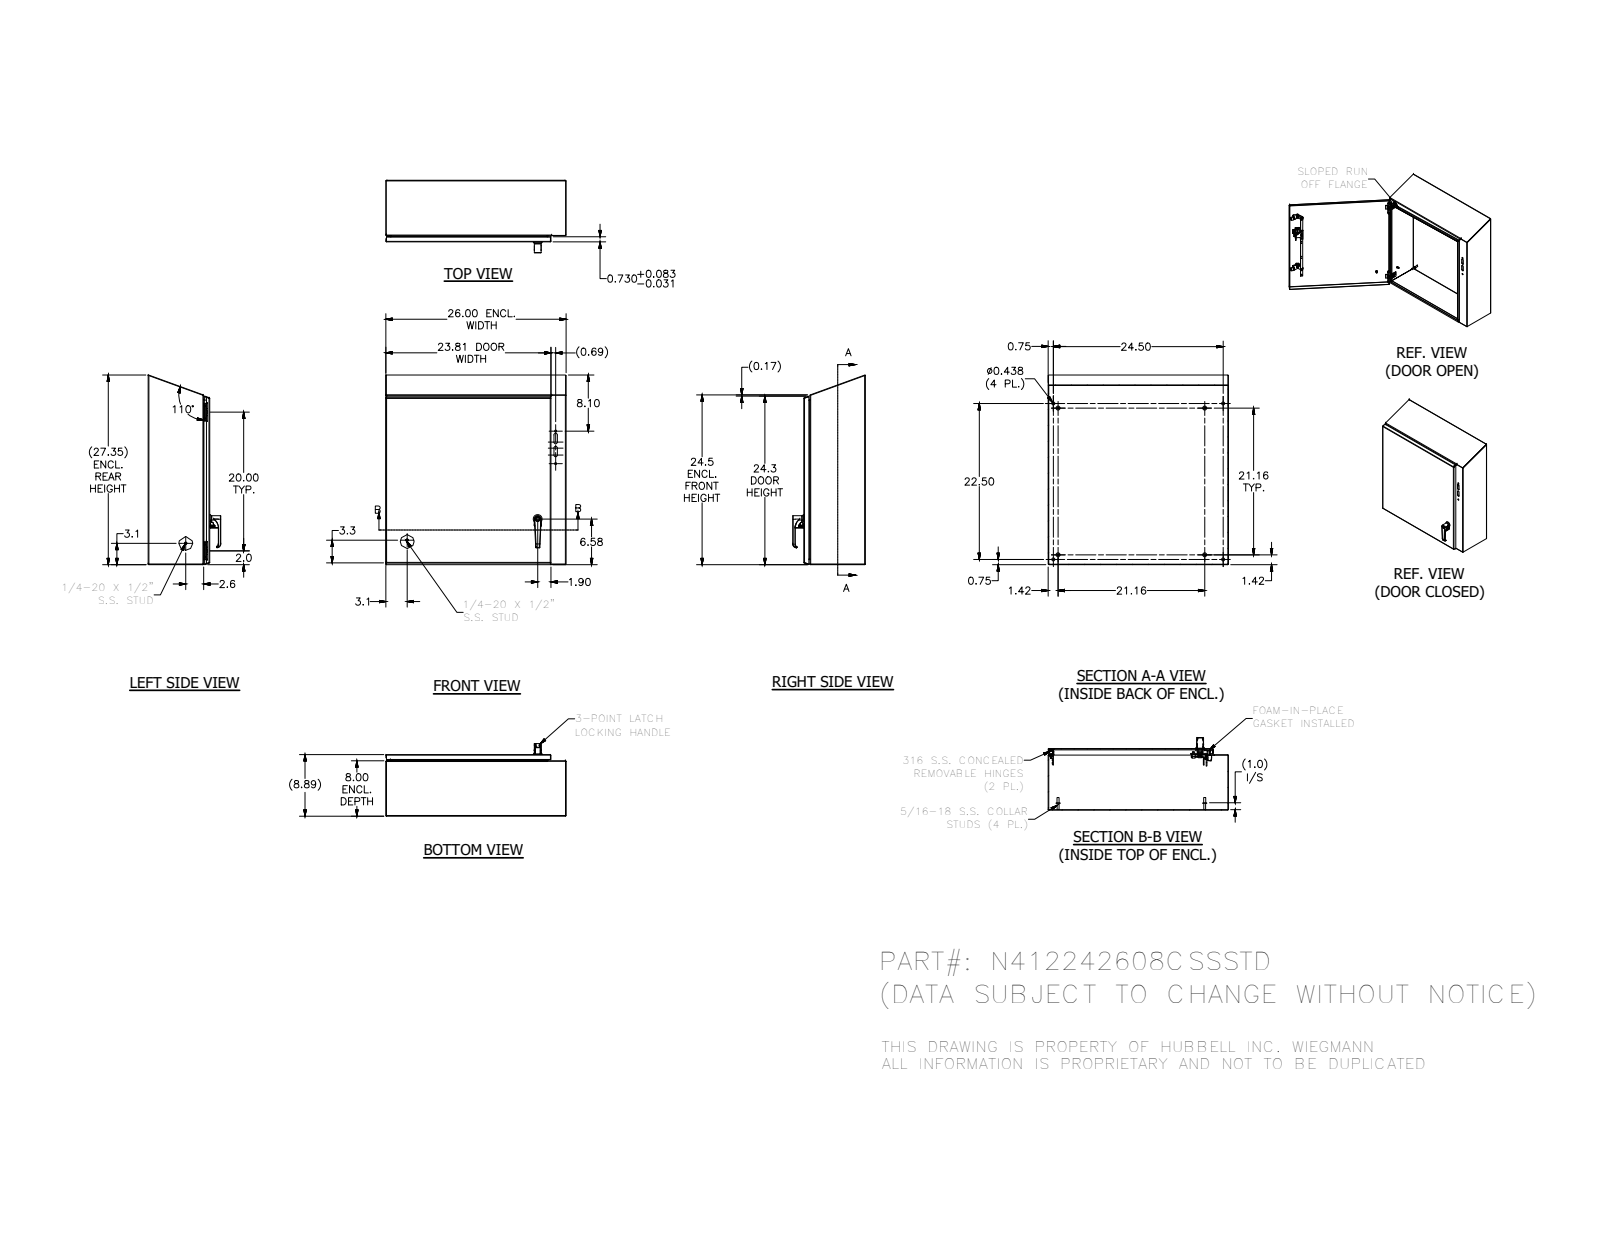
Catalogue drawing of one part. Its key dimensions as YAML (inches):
part_name: "N412242608CSSSTDB3S; 388151; N4122608CSSSTDTOP; 38846 (+8 more)"
step_written_by: "Autodesk Inventor 2016 (AUTOMOTIVE_DESIGN)"
units: inches
bodies: {solids: 62, faces: 2130, planar: 858, cylindrical: 747, other: 525}
overall_size: [27.348, 26, 10.481]
volume: 178.2
surface_area: 4883
round_holes:
  - {diameter: 0.145, count: 6}
  - {diameter: 0.156, count: 5}
  - {diameter: 0.093, count: 4}
  - {diameter: 0.152, count: 4}
  - {diameter: 0.167, count: 4}
  - {diameter: 0.172, count: 4}
  - {diameter: 0.187, count: 4}
  - {diameter: 0.437, count: 4}
  - {diameter: 0.32, count: 3}
  - {diameter: 0.196, count: 2}
  - {diameter: 0.211, count: 2}
  - {diameter: 0.22, count: 2}
round_bosses_or_shafts:
  - {diameter: 0.25, count: 12}
  - {diameter: 0.3, count: 8}
  - {diameter: 0.563, count: 4}
  - {diameter: 0.437, count: 4}
  - {diameter: 0.36, count: 4}
  - {diameter: 0.32, count: 4}
  - {diameter: 0.275, count: 4}
  - {diameter: 0.256, count: 4}
partial_cylinders:
  - {radius: 0.02, count: 38}
  - {radius: 0.012, count: 30}
  - {radius: 0.031, count: 26}
  - {radius: 0.05, count: 26}
  - {radius: 0.125, count: 25}
  - {radius: 0.016, count: 18}
  - {radius: 0.025, count: 16}
  - {radius: 0.105, count: 16}
face_to_face_distances: [0.074, 8.813, 8.739, 8.887, 25.926, 0.059, 25.852, 26, 7.926, 0.887]
hole_center_spacings: [20, 0.5, 14.625, 14.625, 14.626, 24.9, 0.656, 0.66]
